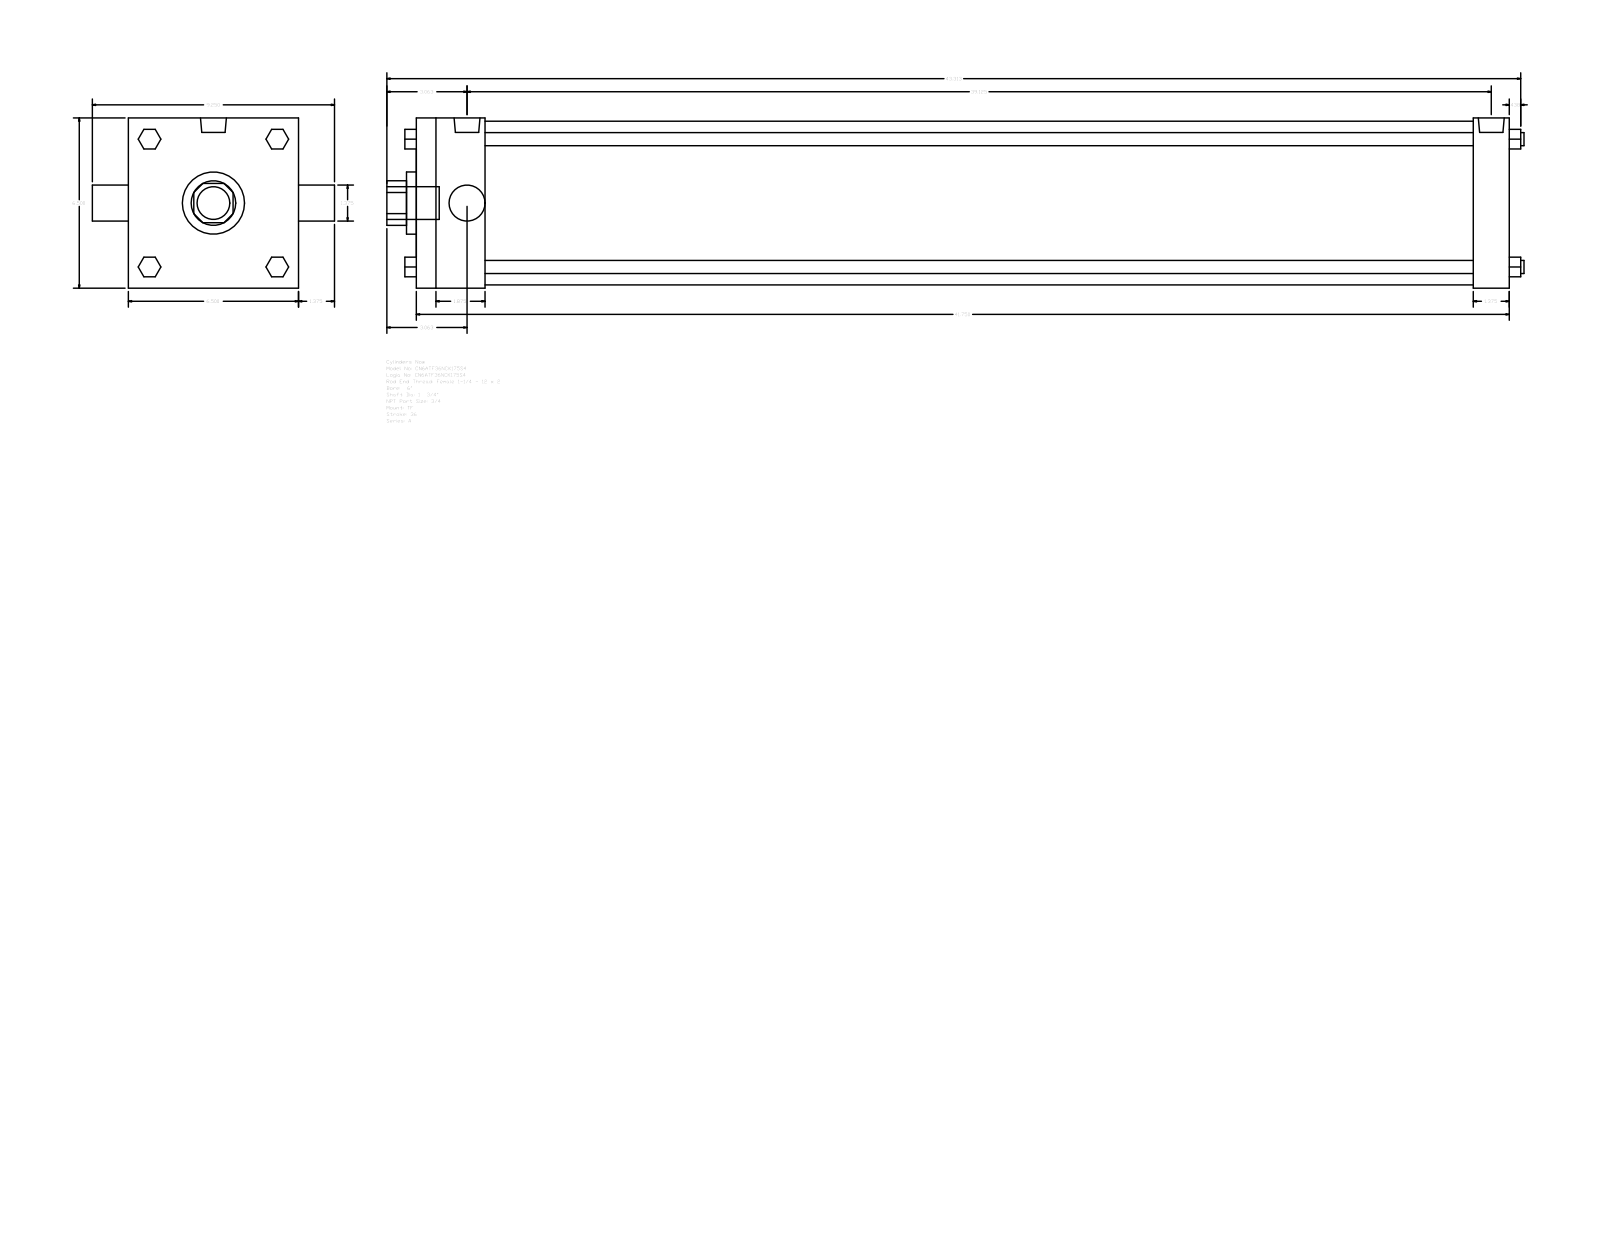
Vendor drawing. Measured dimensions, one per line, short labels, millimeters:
name: A_TF__0600_1.75
written by: GSSL Pune (CONFIG_CONTROL_DESIGN)
unit: mm
bodies: 0 solids, 120 faces (92 planar, 28 cylindrical, 0 other)
size: 1103.31 × 234.95 × 165.1
holes: 1× ⌀34.92, 1× ⌀44.45, 1× ⌀60.33, 1× ⌀158.75
bosses: 4× ⌀12.7, 3× ⌀15.08, 2× ⌀25.12, 1× ⌀31.75
rounds: 1× R21.63
face distances: 165.1, 1060.46, 66.68, 993.78, 1025.53, 958.85, 34.93, 19.05, 34.92, 61.97
